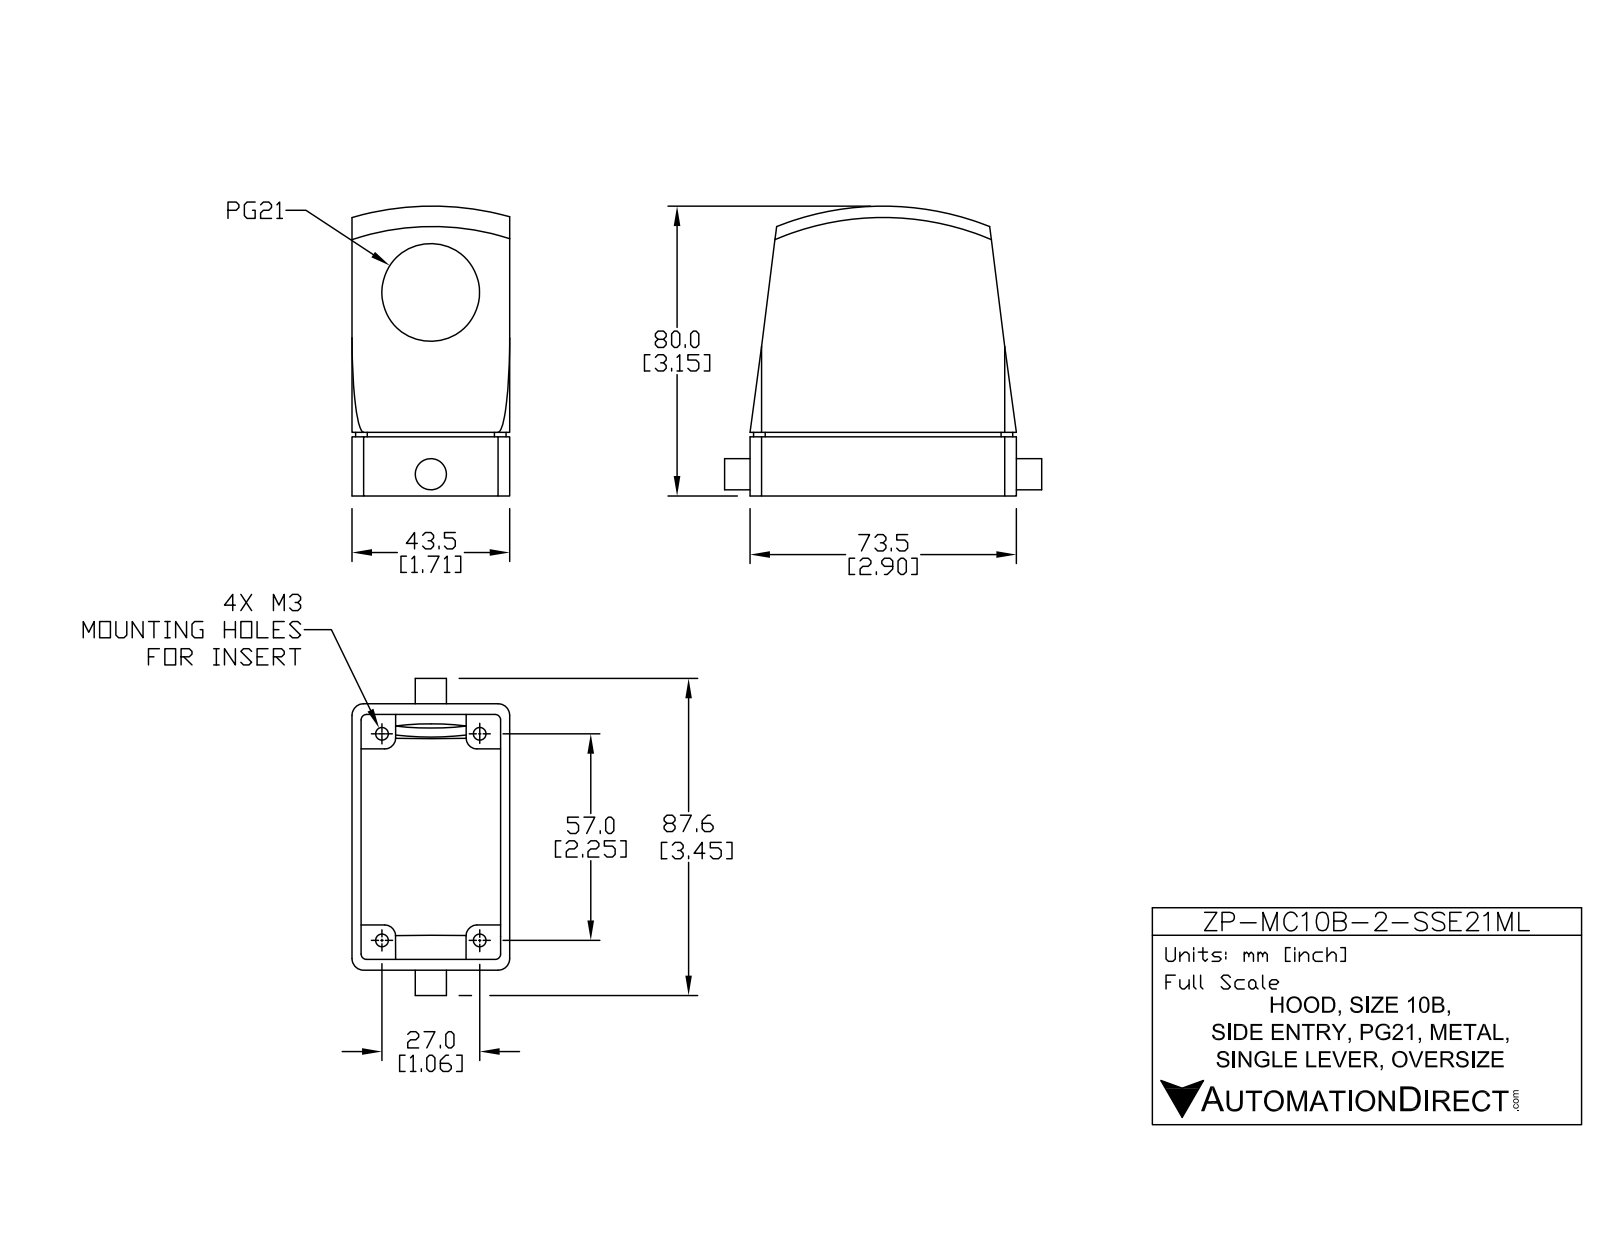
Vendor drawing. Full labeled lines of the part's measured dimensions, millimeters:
Part name (STEP PRODUCT): ZP-MC10B-2-SSE21ML
STEP written by: SolidWorks 2011 (AUTOMOTIVE_DESIGN)
Units: millimetres
Bodies: 5 solids, 92 faces (54 planar, 32 cylindrical, 6 other)
Overall size (bounding box): 87.5 × 77.55 × 43.5
Volume: 57 919 mm³ · Surface area: 43 821 mm²
Round holes (diameter × count): ⌀3.5 ×4, ⌀27 ×1
Round bosses / shafts (diameter × count): ⌀8.6 ×1
Partial cylindrical surfaces — rounded edges, fillets, slot ends (radius × count): R3.2 ×8, R0.7 ×4, R3 ×4
Main face-to-face distances: 2.5, 41, 43.5, 38.5, 9.5, 58.08, 2.96, 12.46, 61.04, 70.54
Hole centre spacings: 28.96, 59, 65.72
